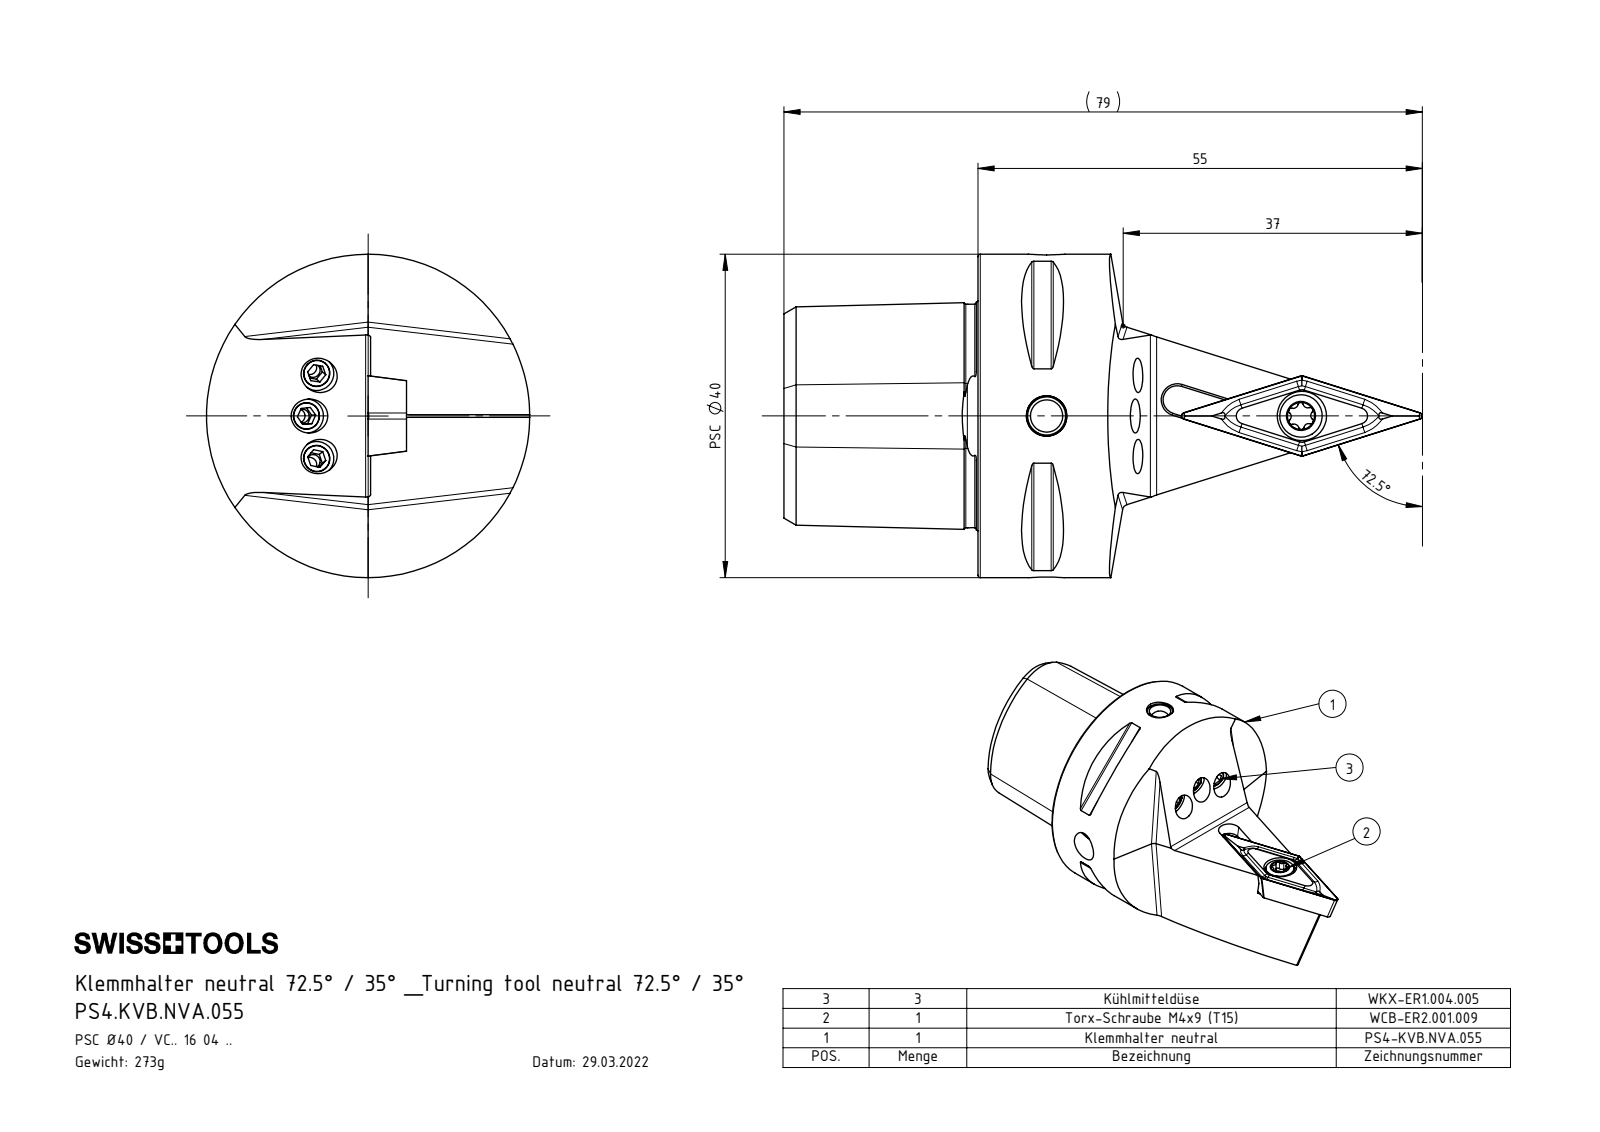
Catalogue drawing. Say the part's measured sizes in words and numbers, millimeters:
The part is named "VCMT160404; PS4.KVB.NVA.055; KVT_MB_600_050; WKX-ER1.004.005_A_PreviewCfg (+2 more)". Its 3-D file was written by "SolidWorks 2017 (AUTOMOTIVE_DESIGN)". It is 12 solids with 431 faces: 89 planar, 114 cylindrical and 228 other. Overall it measures 79 by 40 by 40 millimeters. Its volume is 34 263 cubic millimeters and its surface area 12 783 square millimeters. Round holes: 6 of diameter 4.2, 4 of diameter 3.3, 4 of diameter 4, 3 of diameter 1.7, 2 of diameter 5, 1 of diameter 4.4, 1 of diameter 4.6, 1 of diameter 6.1, 1 of diameter 12.5, 1 of diameter 18, 1 of diameter 20. Round bosses or shafts: 4 of diameter 4, 3 of diameter 5, 1 of diameter 40, 1 of diameter 5.25. Partial cylindrical surfaces (rounded edges, fillets, slot ends): 8 of radius 0.3, 6 of radius 0.34, 6 of radius 0.59, 5 of radius 0.8, 1 of radius 1.75, 1 of radius 5.58. The main face-to-face distances are 24, 4.46, 15.52, 35.3, 9, 0.83, 0.82, 15, 8.63, 4.76. The hole center spacings are 3.5, 20, 23.5, 27.98, 28.09, 31.48, 31.59, 51.48.
